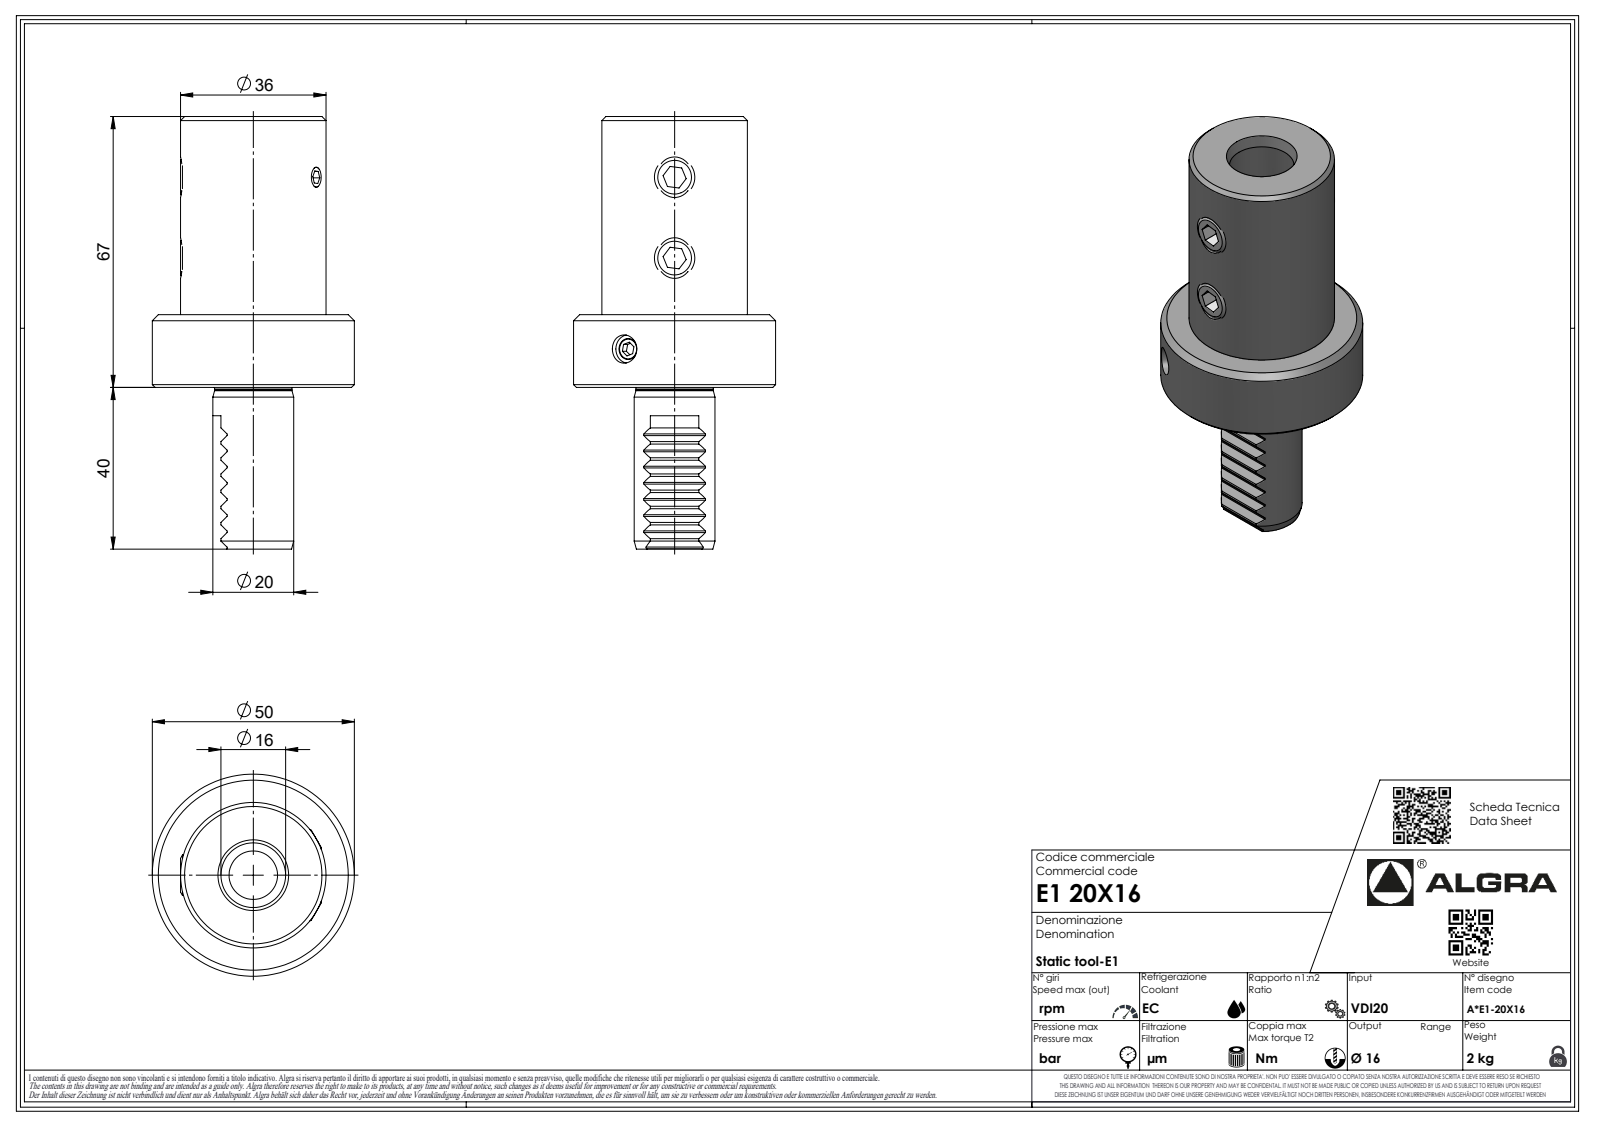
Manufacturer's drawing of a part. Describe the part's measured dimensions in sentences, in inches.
The part is named "E120X16". Its 3-D file was written by "SolidWorks 2023 (AUTOMOTIVE_DESIGN)". It is 1 solid with 258 faces: 175 planar, 42 cylindrical and 41 other. Overall it measures 4.213 by 1.969 by 1.969 inches. Its volume is 5.893 cubic inches and its surface area 22.82 square inches. Round holes: 1 of diameter 0.083. Round bosses or shafts: 1 of diameter 1.969, 1 of diameter 1.417, 1 of diameter 0.787, 1 of diameter 0.752, 1 of diameter 0.251, 1 of diameter 0.067. Partial cylindrical surfaces (rounded edges, fillets, slot ends): 8 of radius 0.012, 7 of radius 0.013, 7 of radius 0.02, 7 of radius 0.146, 2 of radius 0.197, 1 of radius 0.008. The main face-to-face distances are 2.638, 0.709, 1.929, 0.111, 1.575, 2.283, 4.213, 0.223, 0.557, 0.334.
